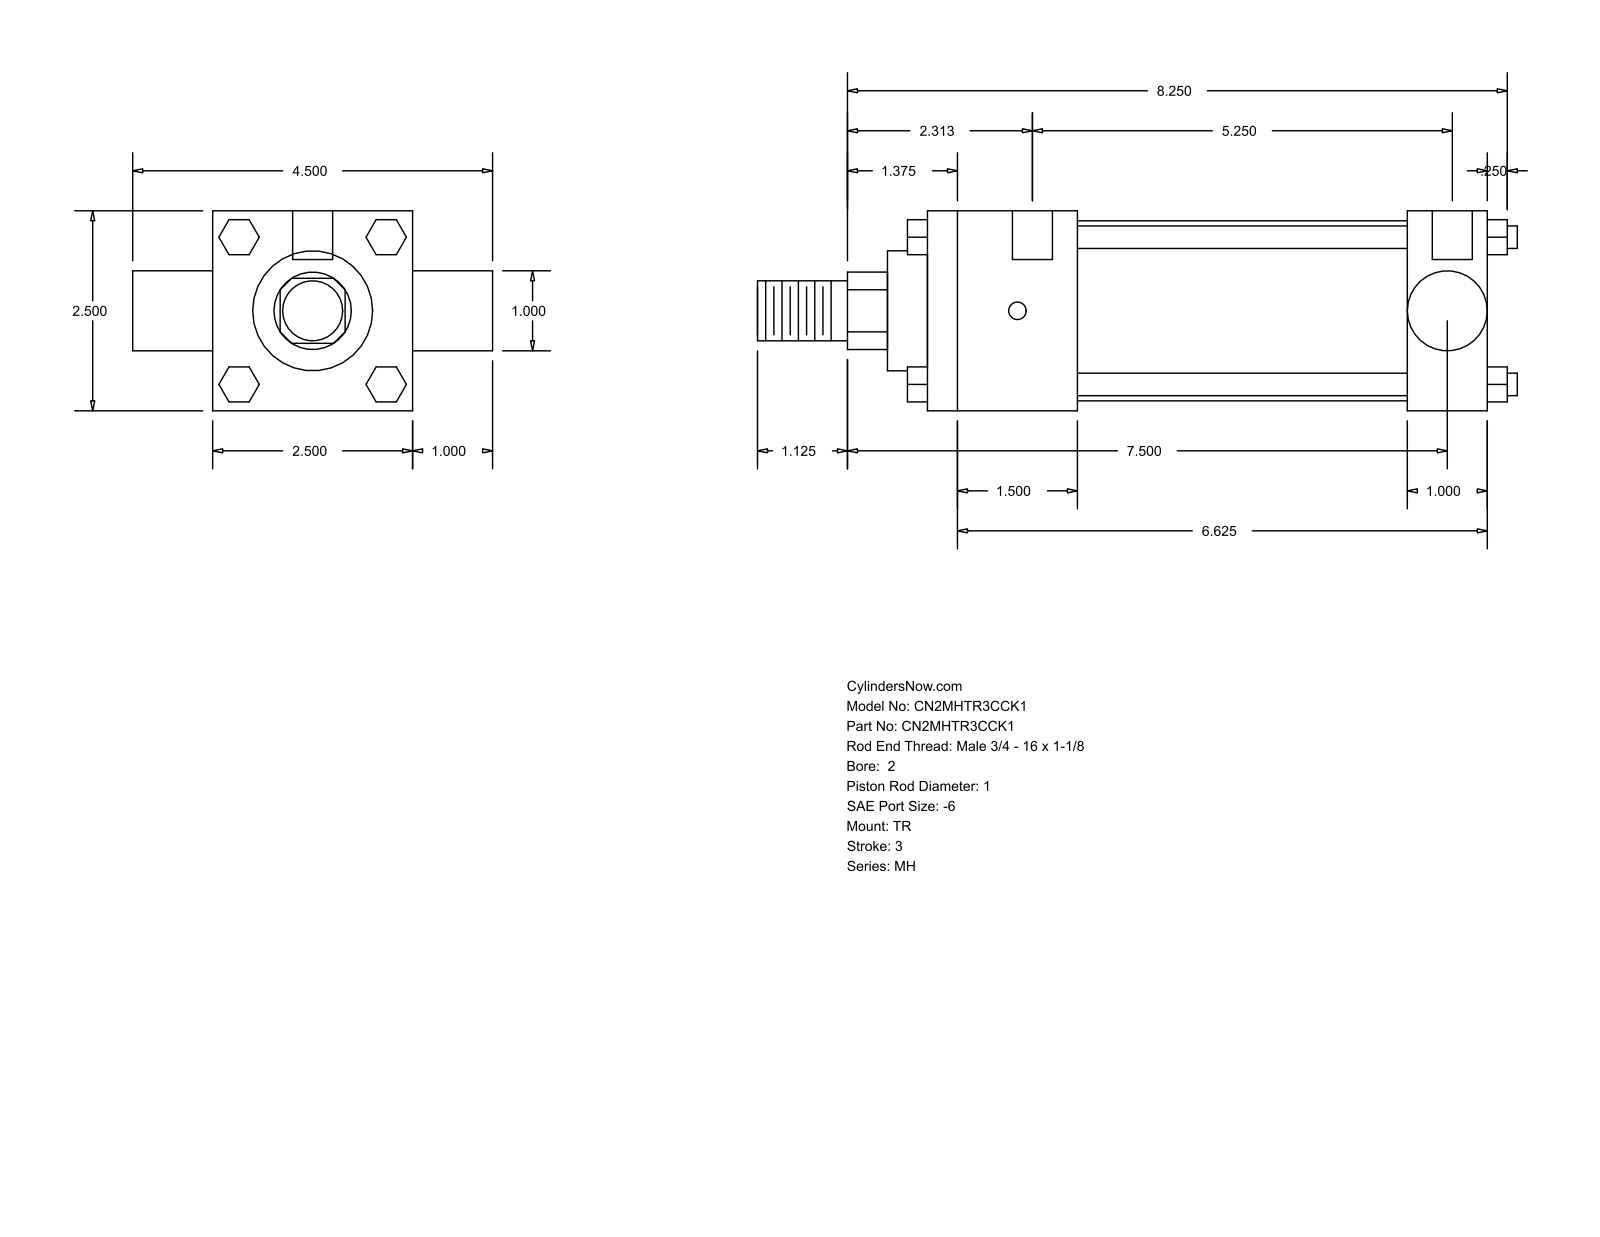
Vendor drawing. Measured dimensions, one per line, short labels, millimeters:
name: MH_TR__0200_1
written by: GSSL Pune (CONFIG_CONTROL_DESIGN)
unit: mm
bodies: 0 solids, 120 faces (92 planar, 28 cylindrical, 0 other)
size: 241.3 × 114.3 × 63.5
holes: 3× ⌀5.56, 2× ⌀12.7
bosses: 4× ⌀7.14, 1× ⌀57.15, 1× ⌀38.1, 1× ⌀25.4, 1× ⌀25.35, 1× ⌀19.05
rounds: 1× R12.29
face distances: 63.5, 177.8, 25.4, 47.63, 152.4, 104.77, 130.17, 88.9, 190.5, 6.35
hole spacings: 3.17, 4.76, 133.35, 136.52, 138.11, 141.28
